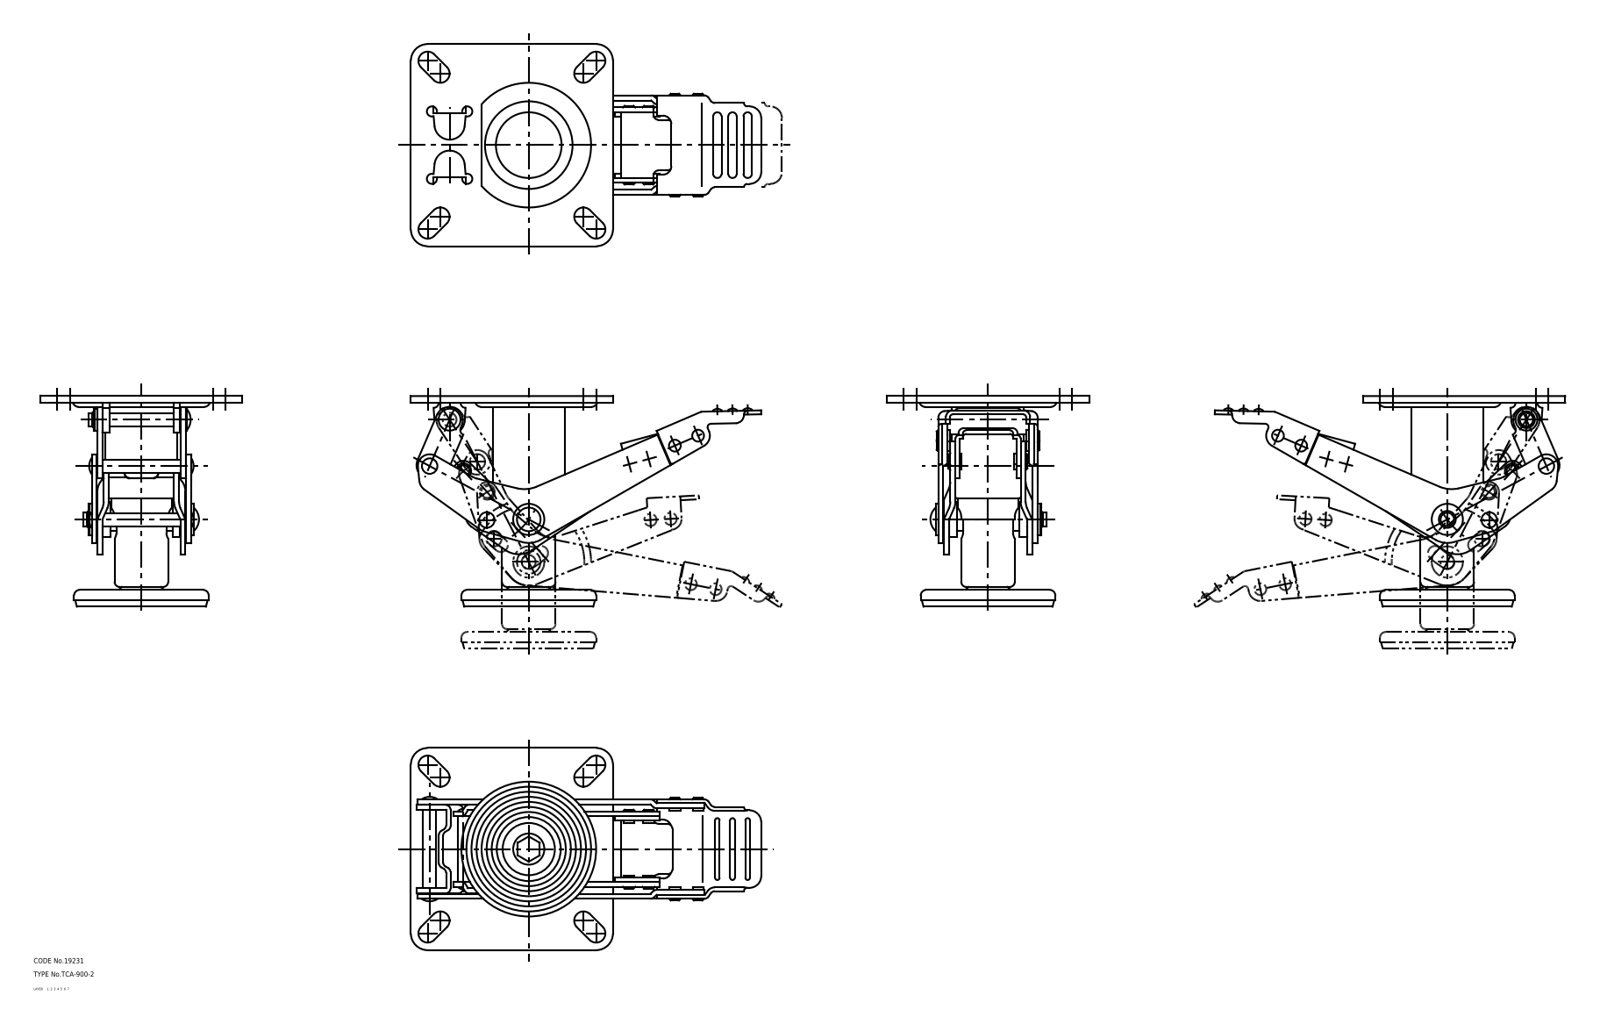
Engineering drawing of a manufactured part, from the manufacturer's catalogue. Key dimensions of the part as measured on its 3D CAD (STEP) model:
Part name (STEP PRODUCT): pedal_A; support rod_B; support rod_A; pedal_B (+3 more)
STEP written by: CADfix (AUTOMOTIVE_DESIGN)
Units: millimetres
Bodies: 6 solids, 535 faces (0 planar, 0 cylindrical, 535 other)
Overall size (bounding box): 208.03 × 125 × 120
Volume: 225 592 mm³ · Surface area: 141 426 mm²
